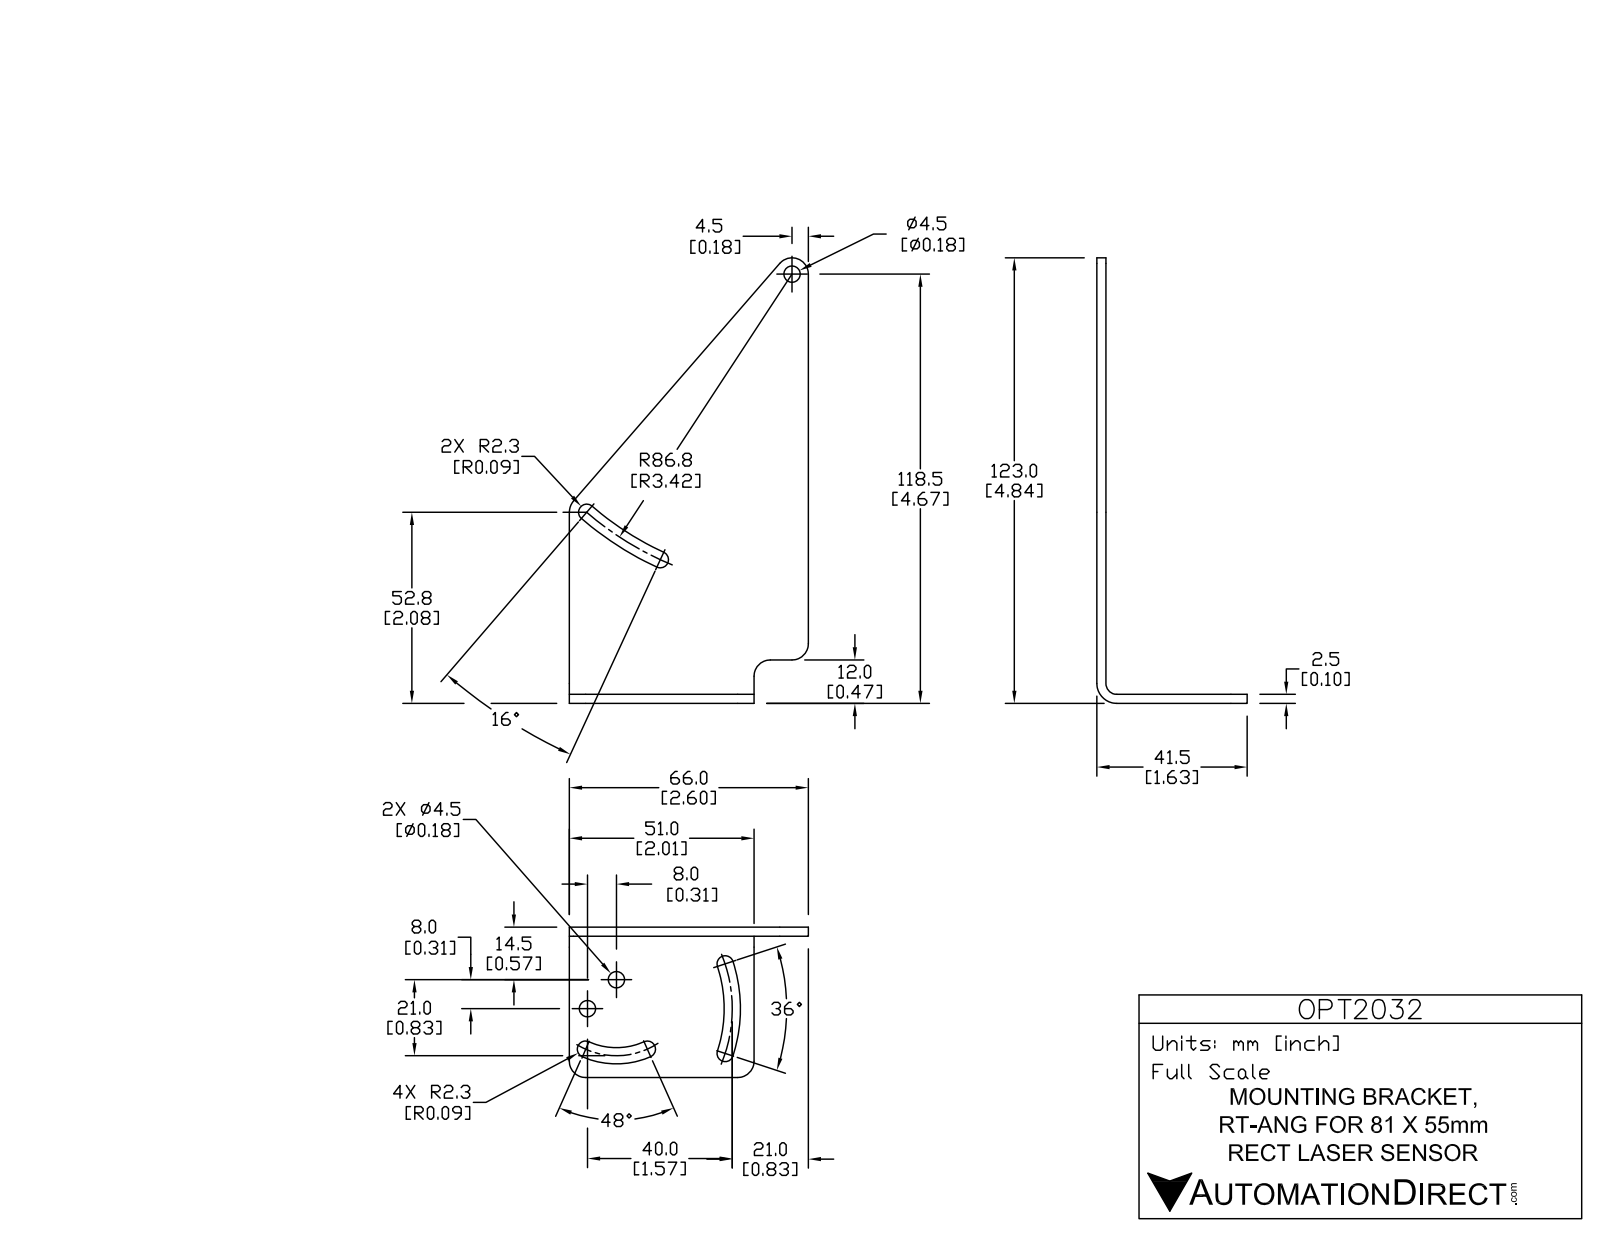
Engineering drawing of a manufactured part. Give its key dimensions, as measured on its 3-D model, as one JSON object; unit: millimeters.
{"part_name": "OPT2032", "step_written_by": "SolidWorks 2013 (AUTOMOTIVE_DESIGN)", "units": "millimeters", "bodies": {"solids": 1, "faces": 41, "planar": 10, "cylindrical": 31, "other": 0}, "overall_size": [123, 66, 41.5], "volume_mm3": 18471, "surface_area_mm2": 16336, "round_holes": [[4.5, 3]], "partial_cylinders_radius": [[2.25, 6], [4.5, 5], [3, 1], [4.8, 1], [5.5, 1], [18.75, 1], [23.25, 1], [37.75, 1]], "face_to_face_distances": [2.5, 66, 39, 41.5, 51, 15, 12, 9.5], "hole_center_spacings": [11.31]}
